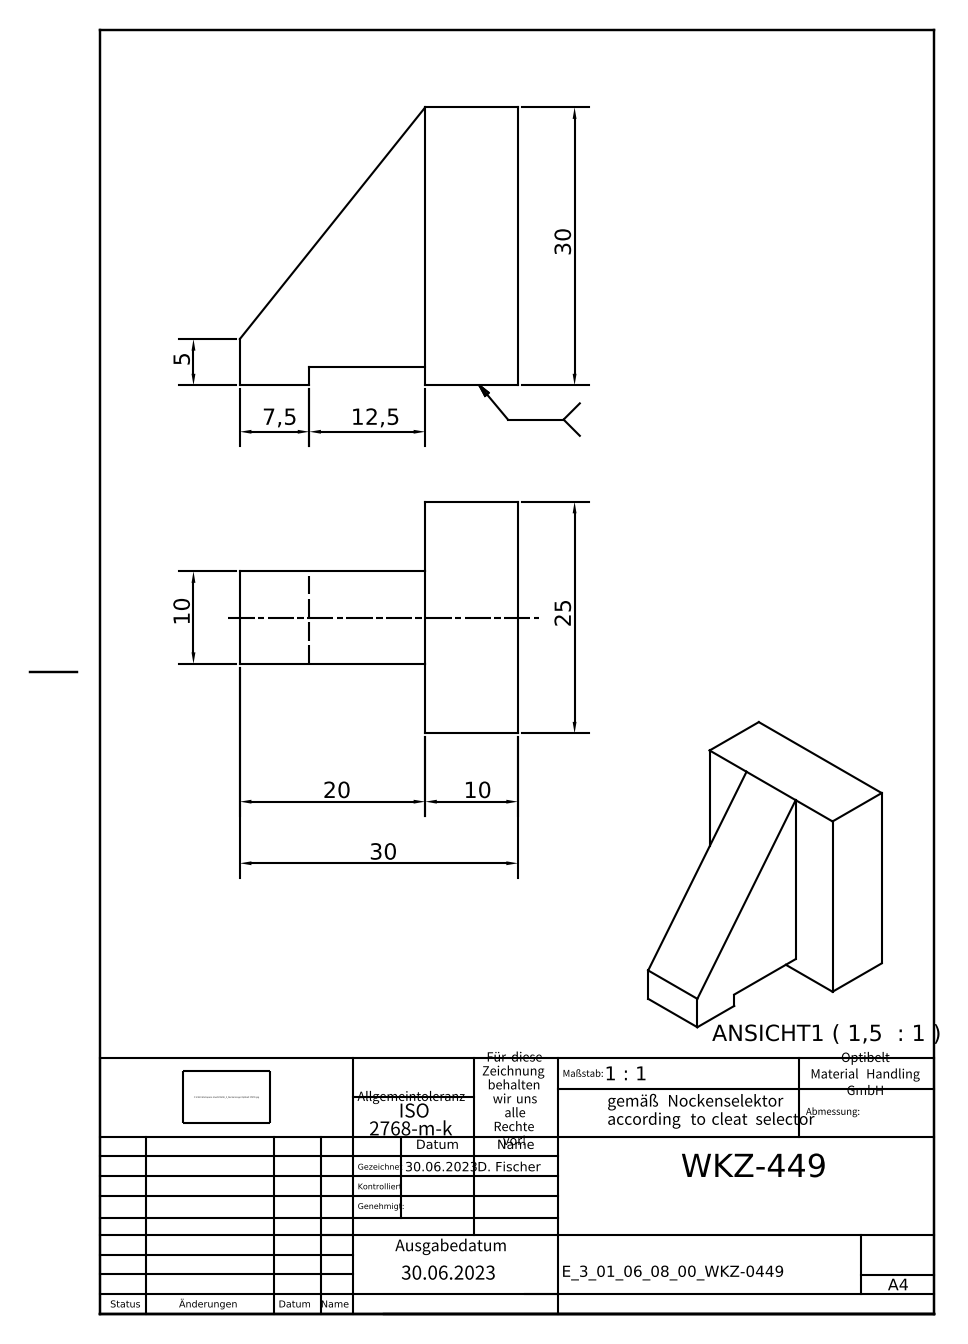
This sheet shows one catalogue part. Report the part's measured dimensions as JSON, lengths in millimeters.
{"part_name": "E_3_01_06_08_00_WKZ-0449", "step_written_by": "Autodesk Inventor 2025 (AUTOMOTIVE_DESIGN)", "units": "millimeters", "bodies": {"solids": 1, "faces": 13, "planar": 13, "cylindrical": 0, "other": 0}, "overall_size": [30, 30, 25], "volume_mm3": 10750, "surface_area_mm2": 3560, "face_to_face_distances": [10, 7.5, 17.5, 25, 30, 2, 28, 20, 12.5, 22.5]}
